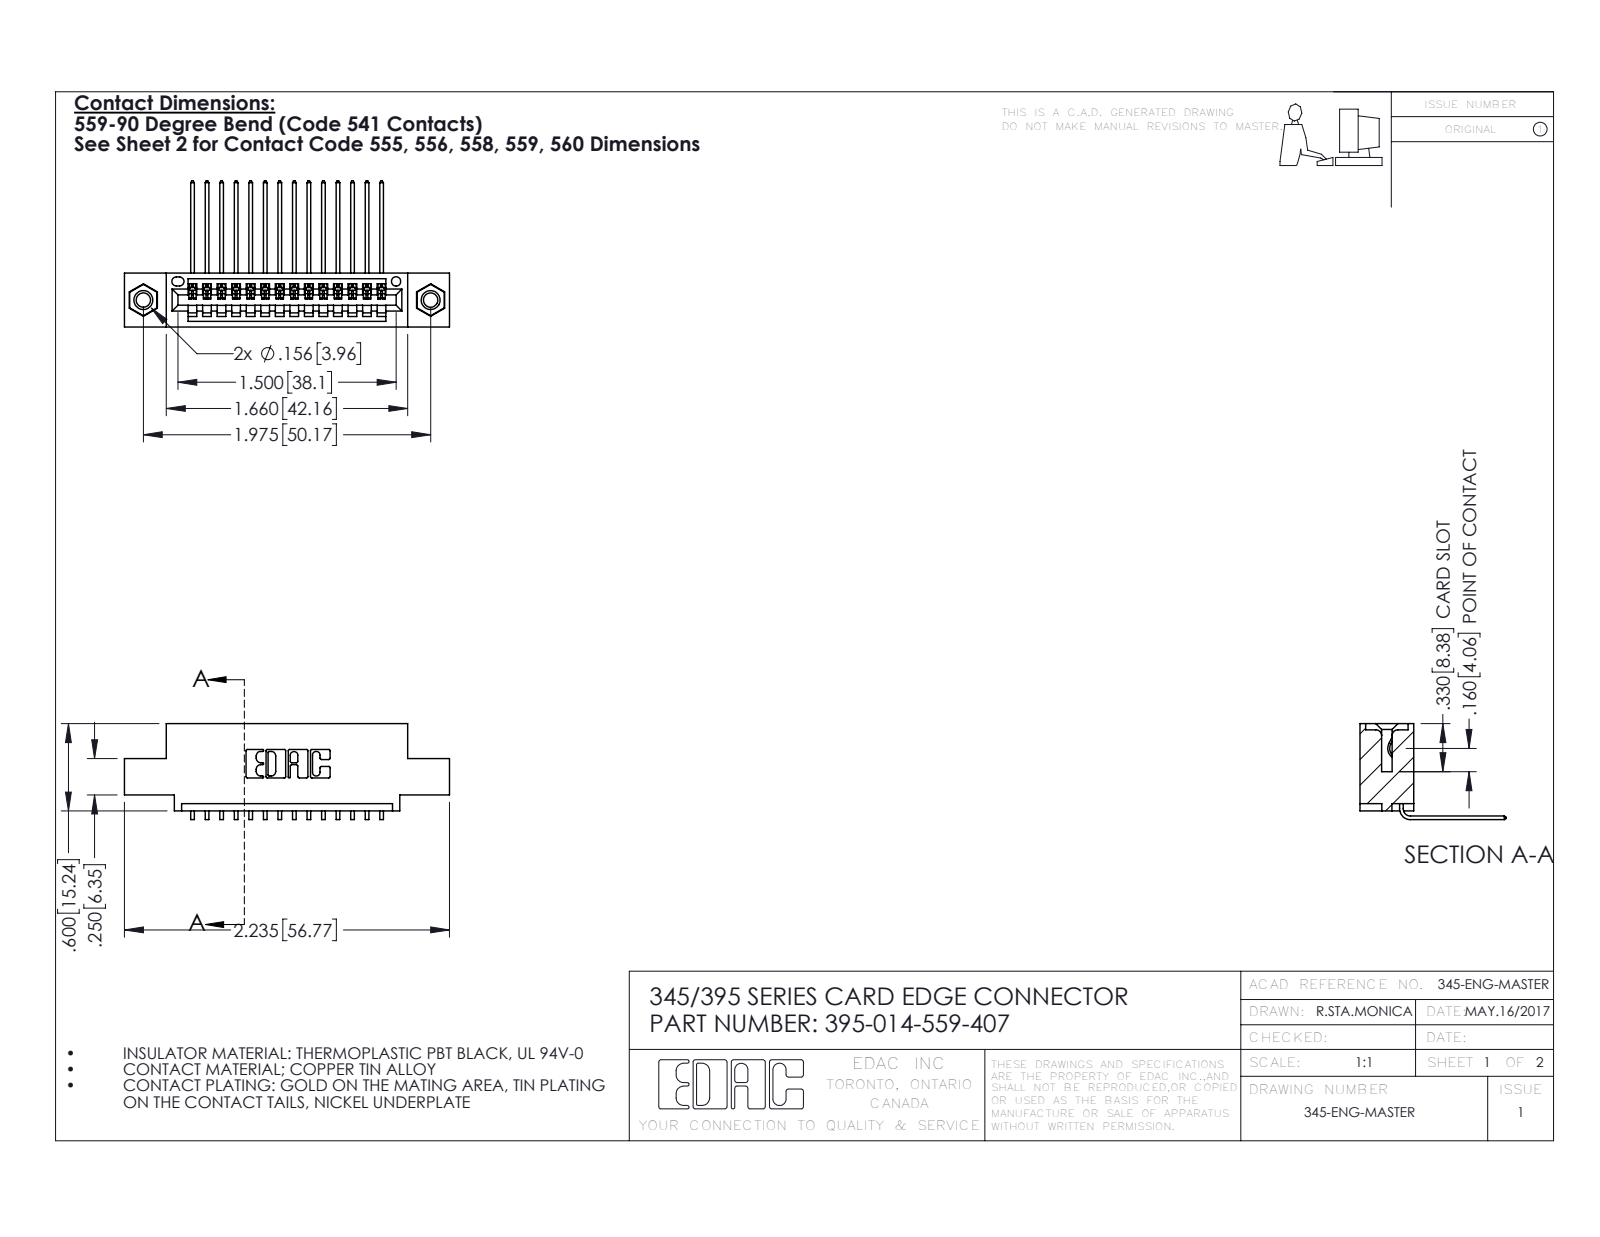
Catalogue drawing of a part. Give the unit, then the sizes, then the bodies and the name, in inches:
Units: inches
Overall size (bounding box): 2.235 × 1.005 × 0.659
Round holes (diameter × count): ⌀0.098 ×2, ⌀0.125 ×2, ⌀0.156 ×2, ⌀0.064 ×1
Round bosses / shafts (diameter × count): ⌀0.155 ×2
Partial cylindrical surfaces — rounded edges, fillets, slot ends (radius × count): R0.006 ×28, R0.01 ×22, R0.007 ×6, R0.031 ×6, R0.026 ×3, R0.031 ×2, R0.04 ×2, R0.014 ×1
Main face-to-face distances: 0.072, 0.298, 0.37, 0.2, 0.098, 0.272, 0.025, 0.225, 0.1, 0.3
Hole centre spacings: 0.27, 1.742, 1.975
Volume: 0.313 in³ · Surface area: 10.56 in²
Bodies: 17 solids, 1030 faces (704 planar, 310 cylindrical, 16 other)
Part name (STEP PRODUCT): 395-014-559-407; 345 Part_0.110 Offset - 0.156 Dia-TI; 345-292-001_558 559 Tail - 1; 345-250-001_345-250-005-103
STEP written by: SolidWorks 2016 (CONFIG_CONTROL_DESIGN)
